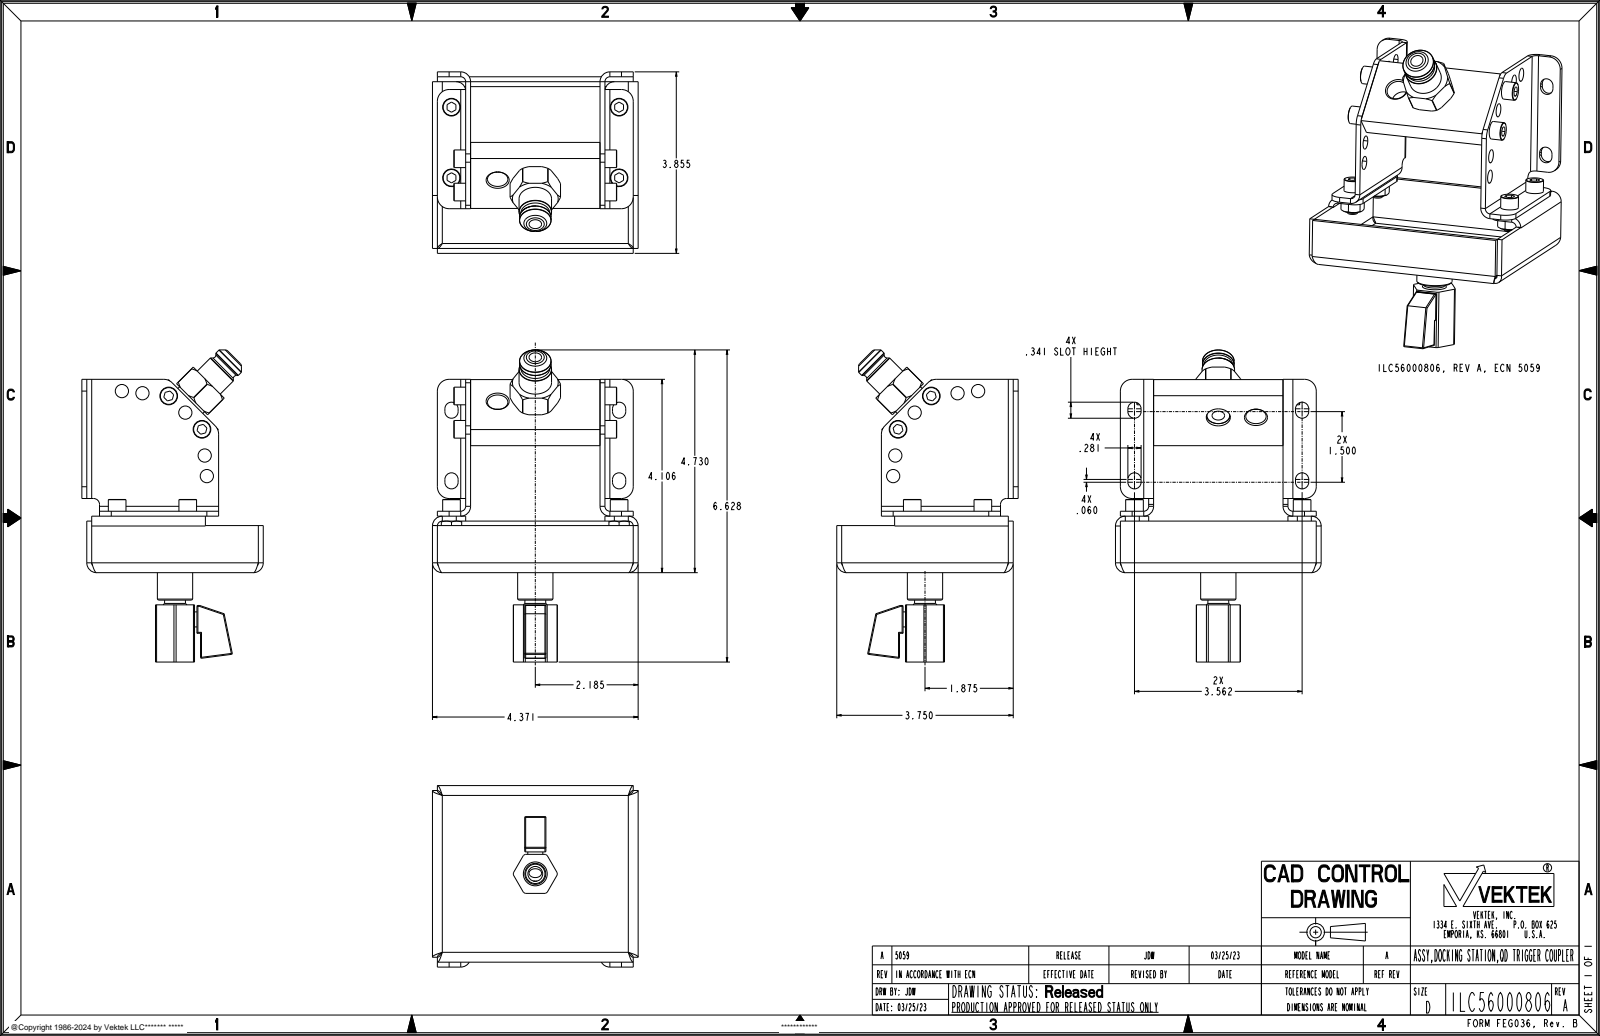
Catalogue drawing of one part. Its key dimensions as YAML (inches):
part_name: "ILC56000806"
step_written_by: "CREO PARAMETRIC BY PTC INC, 2021164 (AUTOMOTIVE_DESIGN)"
units: inches
bodies: {solids: 3, faces: 528, planar: 226, cylindrical: 158, other: 144}
overall_size: [6.628, 4.371, 3.855]
volume: 9.388
surface_area: 143.5
round_holes:
  - {diameter: 0.281, count: 7}
  - {diameter: 0.266, count: 1}
  - {diameter: 0.315, count: 1}
  - {diameter: 0.433, count: 1}
  - {diameter: 0.443, count: 1}
  - {diameter: 0.511, count: 1}
  - {diameter: 0.781, count: 1}
round_bosses_or_shafts:
  - {diameter: 0.375, count: 6}
  - {diameter: 0.25, count: 4}
  - {diameter: 0.75, count: 2}
  - {diameter: 0.252, count: 2}
  - {diameter: 0.69, count: 1}
  - {diameter: 0.671, count: 1}
  - {diameter: 0.319, count: 1}
partial_cylinders:
  - {radius: 0.02, count: 18}
  - {radius: 0.105, count: 10}
  - {radius: 0.209, count: 10}
  - {radius: 0.25, count: 10}
  - {radius: 0.141, count: 8}
  - {radius: 0.2, count: 4}
  - {radius: 0.125, count: 1}
  - {radius: 0.466, count: 1}
face_to_face_distances: [0.105, 2.855, 0.706, 3.561, 0.104, 3.645, 2.75, 2.96, 0.601, 3.456]
hole_center_spacings: [1, 0.439, 0.5, 0.561, 0.8, 1.423, 1.478, 1.885]
